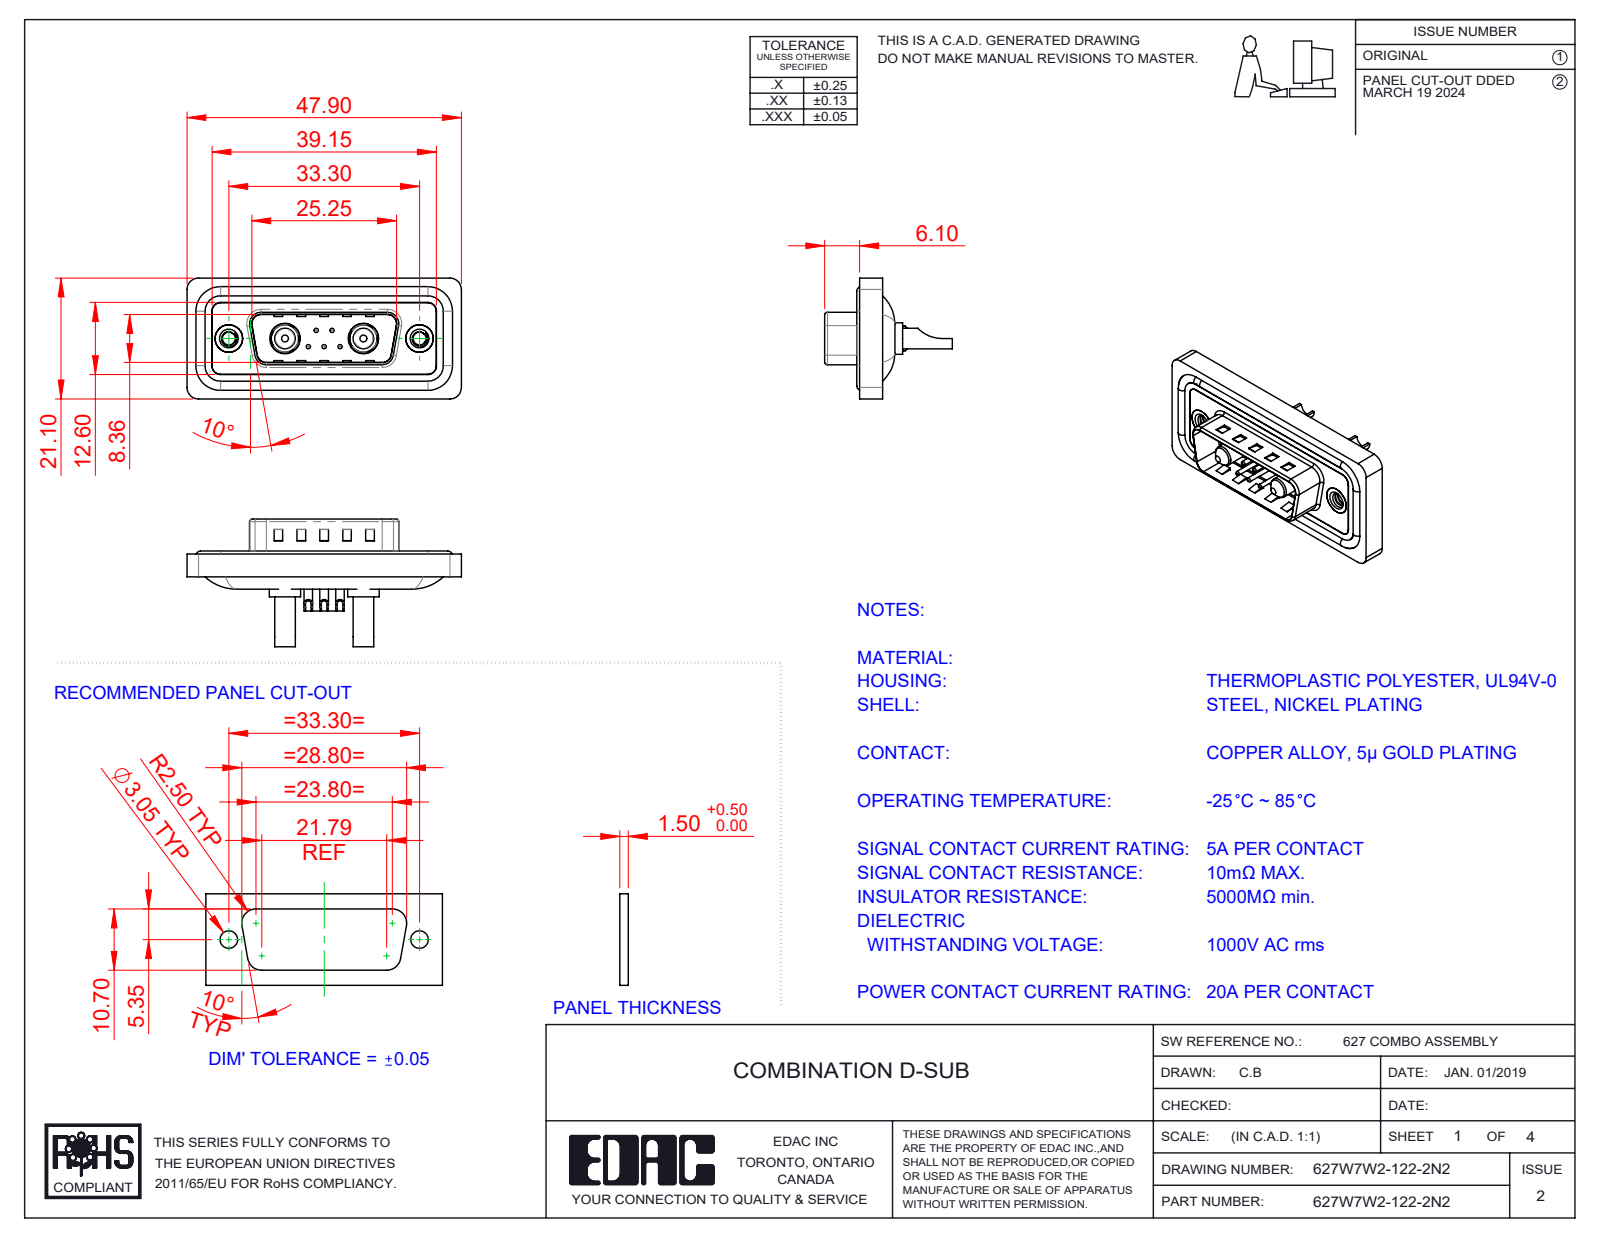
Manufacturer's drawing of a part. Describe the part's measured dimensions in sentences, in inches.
The part is named "627Combo Housing_7W2; 627Combo Shell Rear_15 Contacts; 627W7W2-122-2N2; 627Combo Threaded Rivet_2 (+5 more)". Its 3-D file was written by "SolidWorks 2023 (CONFIG_CONTROL_DESIGN)". It is 16 solids with 722 faces: 248 planar, 308 cylindrical and 166 other. Overall it measures 1.886 by 0.878 by 0.831 inches. Its volume is 0.339 cubic inches and its surface area 13.95 square inches. Round holes: 5 of diameter 0.03, 5 of diameter 0.039, 5 of diameter 0.063, 5 of diameter 0.079, 2 of diameter 0.089, 2 of diameter 0.106, 2 of diameter 0.157, 2 of diameter 0.189, 2 of diameter 0.191, 2 of diameter 0.197, 2 of diameter 0.209. Round bosses or shafts: 5 of diameter 0.059, 4 of diameter 0.063, 2 of diameter 0.217, 2 of diameter 0.205, 2 of diameter 0.193, 2 of diameter 0.187, 2 of diameter 0.148, 2 of diameter 0.142. Partial cylindrical surfaces (rounded edges, fillets, slot ends): 26 of radius 0.059, 20 of radius 0.079, 8 of radius 0.02, 8 of radius 0.063, 6 of radius 0.039, 4 of radius 0.01, 4 of radius 0.024, 4 of radius 0.026. The main face-to-face distances are 0.016, 0.043, 0.063, 0.059, 0.02, 0.122, 0.114, 0.032, 0.377, 0.098. The hole center spacings are 0.124, 0.109, 0.386, 0.925, 0.17, 0.17, 0.198, 0.198.
